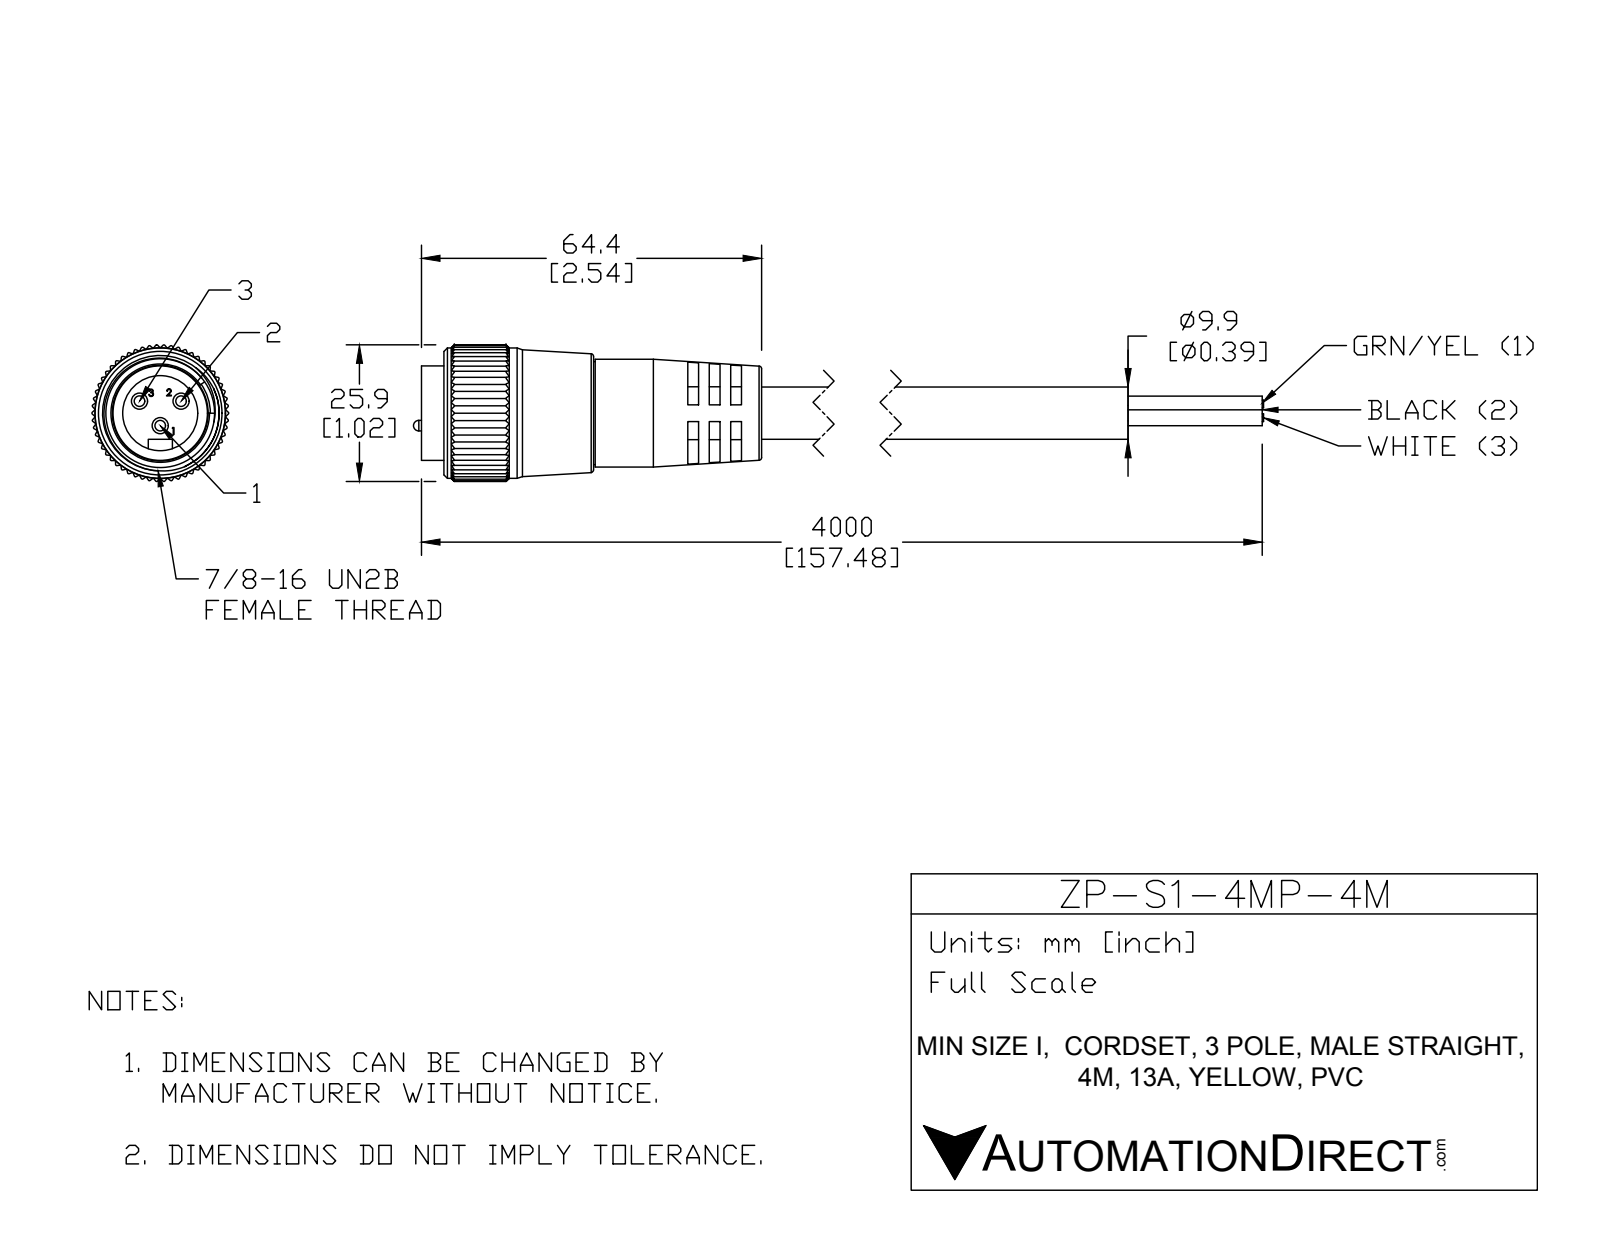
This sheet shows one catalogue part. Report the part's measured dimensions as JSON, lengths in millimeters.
{"part_name": "ZP-S1-3MP-4M", "step_written_by": "SolidWorks 2015 (AUTOMOTIVE_DESIGN)", "units": "millimeters", "bodies": {"solids": 5, "faces": 564, "planar": 196, "cylindrical": 314, "other": 54}, "overall_size": [109.62, 52.91, 25.84], "volume_mm3": 27012, "surface_area_mm2": 12612, "round_holes": [[14.22, 1], [19.96, 1], [20.45, 1], [21, 1]], "round_bosses_or_shafts": [[3.05, 3], [2, 3], [9.91, 2], [24.68, 1], [20.4, 1], [19.5, 1], [17.88, 1]], "partial_cylinders_radius": [[0.25, 165], [2.29, 1], [5.25, 1], [12.93, 1]], "face_to_face_distances": [2, 4.04, 13.88, 11.88, 2.04, 9.84, 6.04, 7.84, 6.06, 8.06]}
